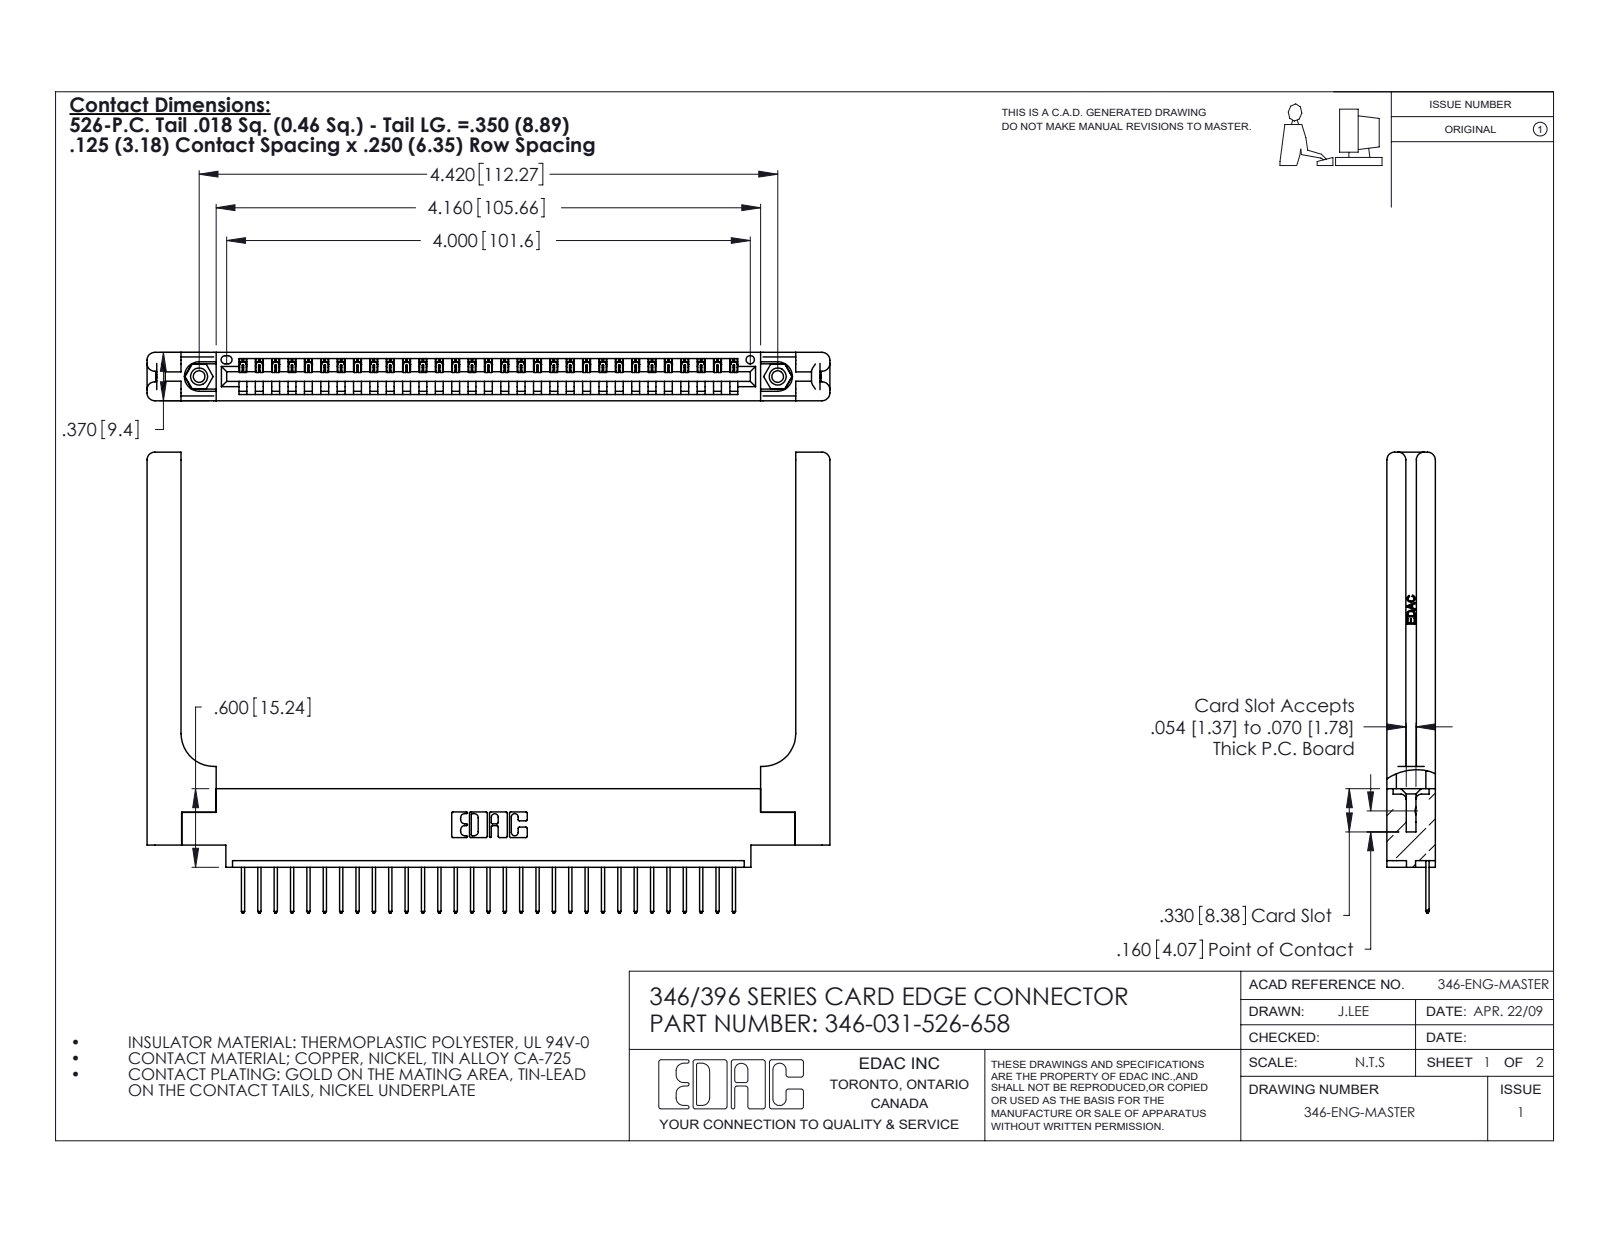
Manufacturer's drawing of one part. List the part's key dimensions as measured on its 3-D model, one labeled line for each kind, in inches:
Part name (STEP PRODUCT): 346-031-526-658; 345-250-001_345-250-001-102; 346 Part_0.170 Offset - 0.156 Dia-TH; 346-220-058_345-220-058 (+1 more)
STEP written by: SolidWorks 2020 (CONFIG_CONTROL_DESIGN)
Units: inches
Bodies: 36 solids, 2194 faces (1482 planar, 652 cylindrical, 60 other)
Overall size (bounding box): 5.216 × 3.52 × 0.37
Volume: 1.216 in³ · Surface area: 32.12 in²
Round holes (diameter × count): ⌀0.089 ×2, ⌀0.125 ×2, ⌀0.156 ×2, ⌀0.064 ×1
Round bosses / shafts (diameter × count): ⌀0.155 ×2
Partial cylindrical surfaces — rounded edges, fillets, slot ends (radius × count): R0.006 ×62, R0.01 ×62, R0.01 ×22, R0.06 ×16, R0.007 ×6, R0.031 ×6, R0.026 ×3, R0.03 ×2
Main face-to-face distances: 0.37, 0.072, 0.048, 0.322, 0.148, 0.15, 0.25, 0.298, 0.025, 0.222
Hole centre spacings: 0.246, 4.212, 4.42
